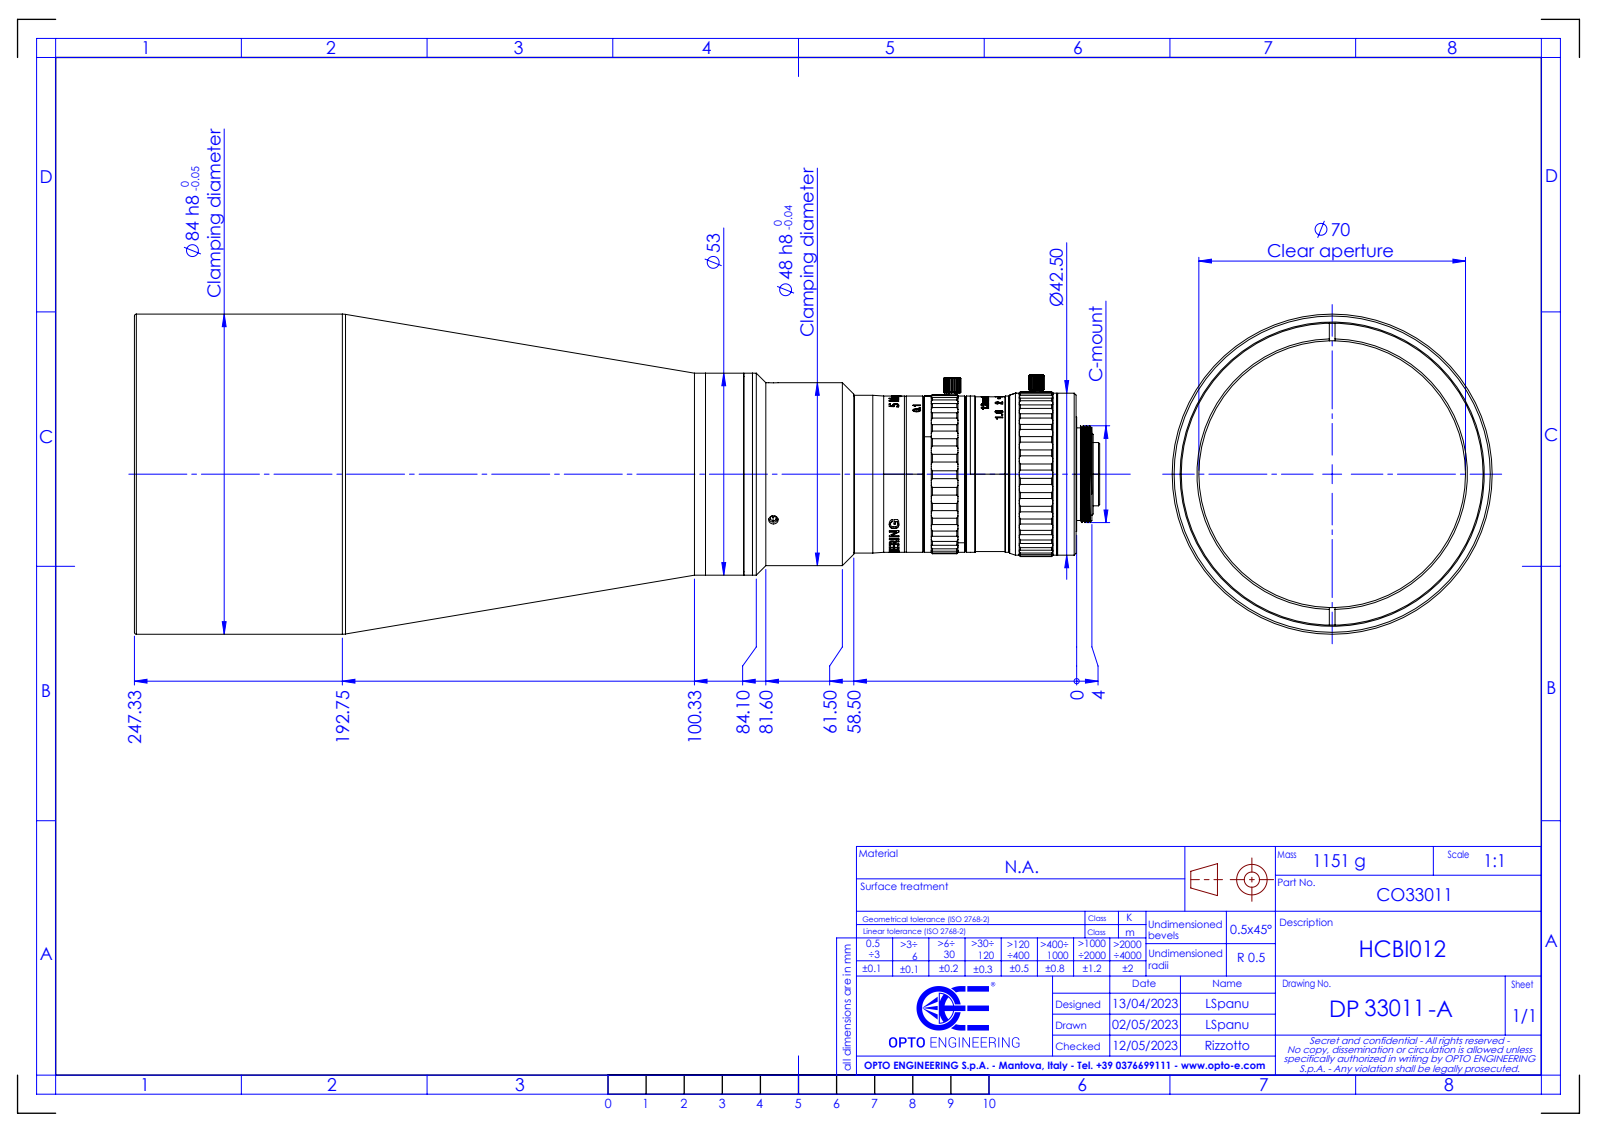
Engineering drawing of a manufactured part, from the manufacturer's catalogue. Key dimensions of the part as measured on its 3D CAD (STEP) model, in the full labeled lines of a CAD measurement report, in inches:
Part name (STEP PRODUCT): DP33011-A_HCBI012
STEP written by: SolidWorks 2021 (CONFIG_CONTROL_DESIGN)
Units: inches
Bodies: 0 solids, 566 faces (89 planar, 310 cylindrical, 167 other)
Overall size (bounding box): 9.976 × 3.307 × 3.307
Round holes (diameter × count): ⌀0.098 ×3, ⌀0.102 ×2, ⌀0.512 ×1, ⌀2.756 ×1, ⌀3.12 ×1
Round bosses / shafts (diameter × count): ⌀3.307 ×1, ⌀2.087 ×1, ⌀1.89 ×1, ⌀1.673 ×1, ⌀1.63 ×1, ⌀1.614 ×1, ⌀1.61 ×1, ⌀1.598 ×1
Partial cylindrical surfaces — rounded edges, fillets, slot ends (radius × count): R0.079 ×67, R0.051 ×1, R0.089 ×1, R0.798 ×1, R0.802 ×1, R0.803 ×1, R0.807 ×1, R0.823 ×1
Main face-to-face distances: 6.259, 0.108, 6.367, 9.712, 9.604, 3.344, 6.28, 6.171, 0.088, 3.432
Hole centre spacings: 0.689, 1.194
